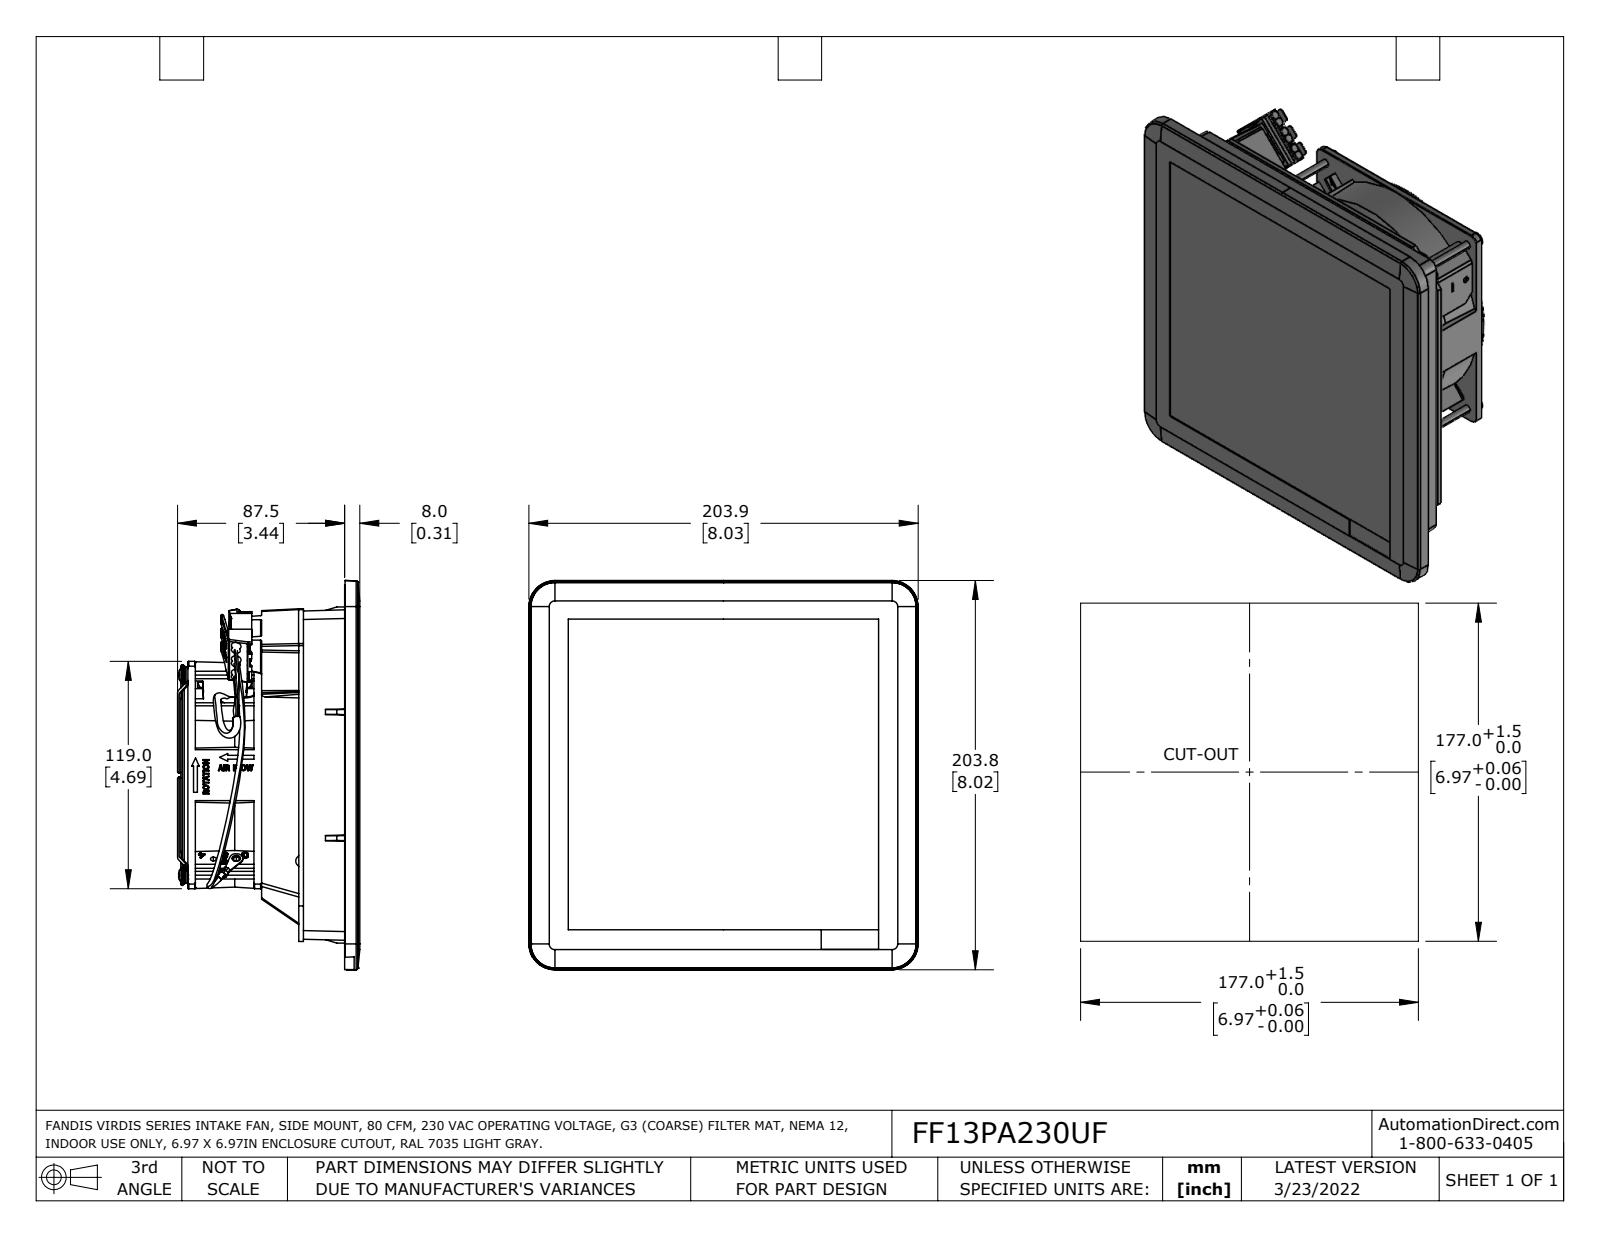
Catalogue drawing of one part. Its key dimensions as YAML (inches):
part_name: "FF13PAxxxyF (p.c.)"
step_written_by: "SolidWorks 2021 (AUTOMOTIVE_DESIGN)"
units: inches
bodies: {solids: 12, faces: 1675, planar: 1026, cylindrical: 321, other: 328}
overall_size: [8.028, 8.027, 3.76]
volume: 115.9
surface_area: 260
round_holes:
  - {diameter: 0.169, count: 6}
  - {diameter: 0.118, count: 4}
  - {diameter: 0.138, count: 2}
  - {diameter: 0.173, count: 1}
round_bosses_or_shafts:
  - {diameter: 0.315, count: 4}
  - {diameter: 0.157, count: 4}
  - {diameter: 0.039, count: 1}
partial_cylinders:
  - {radius: 0.012, count: 42}
  - {radius: 0.02, count: 32}
  - {radius: 0.059, count: 18}
  - {radius: 0.177, count: 14}
  - {radius: 0.016, count: 13}
  - {radius: 0.028, count: 13}
  - {radius: 0.024, count: 9}
  - {radius: 0.118, count: 8}
face_to_face_distances: [3.528, 0.295, 3.232, 0.02, 0.315, 3.547, 1.26, 1.24, 0.945, 2.287]
hole_center_spacings: [0.472, 5.137, 4.126, 5.115, 5.115, 5.835, 0.787, 5.137]
